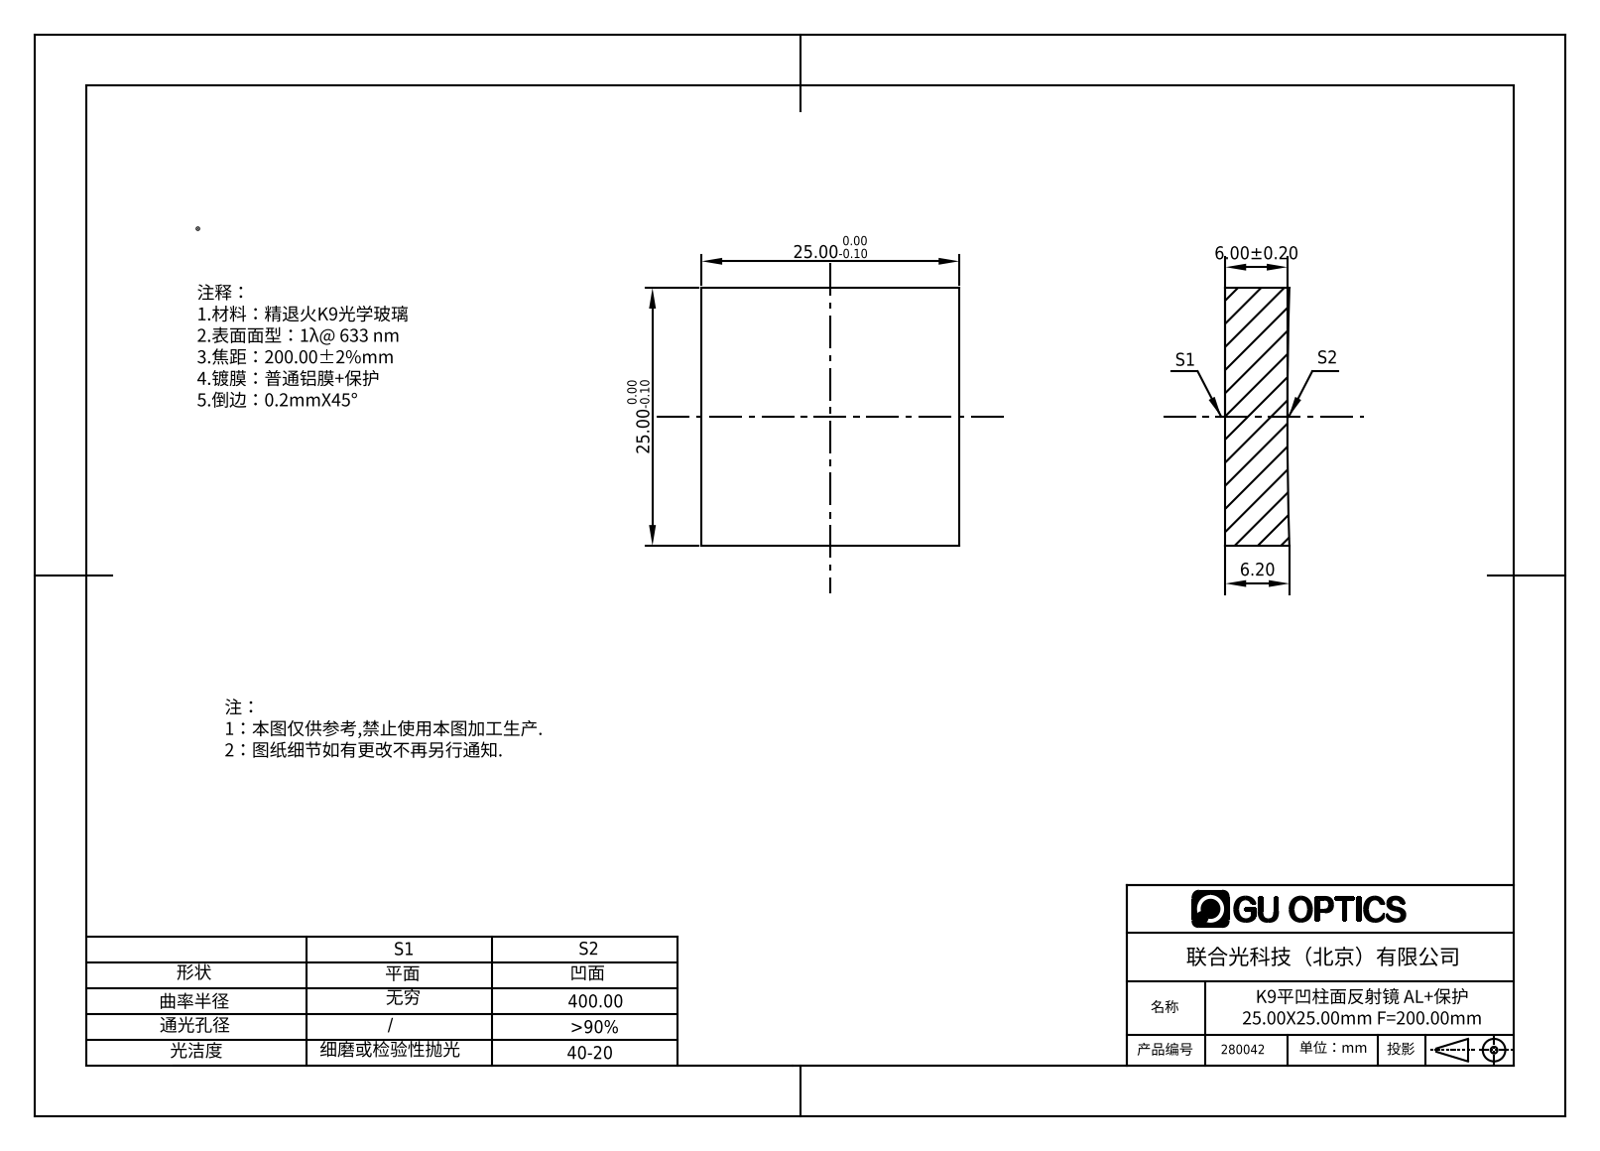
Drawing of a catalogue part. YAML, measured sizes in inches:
part_name: "280020"
step_written_by: "SolidWorks 2016 (AUTOMOTIVE_DESIGN)"
units: inches
bodies: {solids: 1, faces: 7, planar: 5, cylindrical: 2, other: 0}
overall_size: [0.984, 0.984, 0.244]
volume: 0.231
surface_area: 2.888
partial_cylinders:
  - {radius: 15.748, count: 1}
face_to_face_distances: [0.984]
